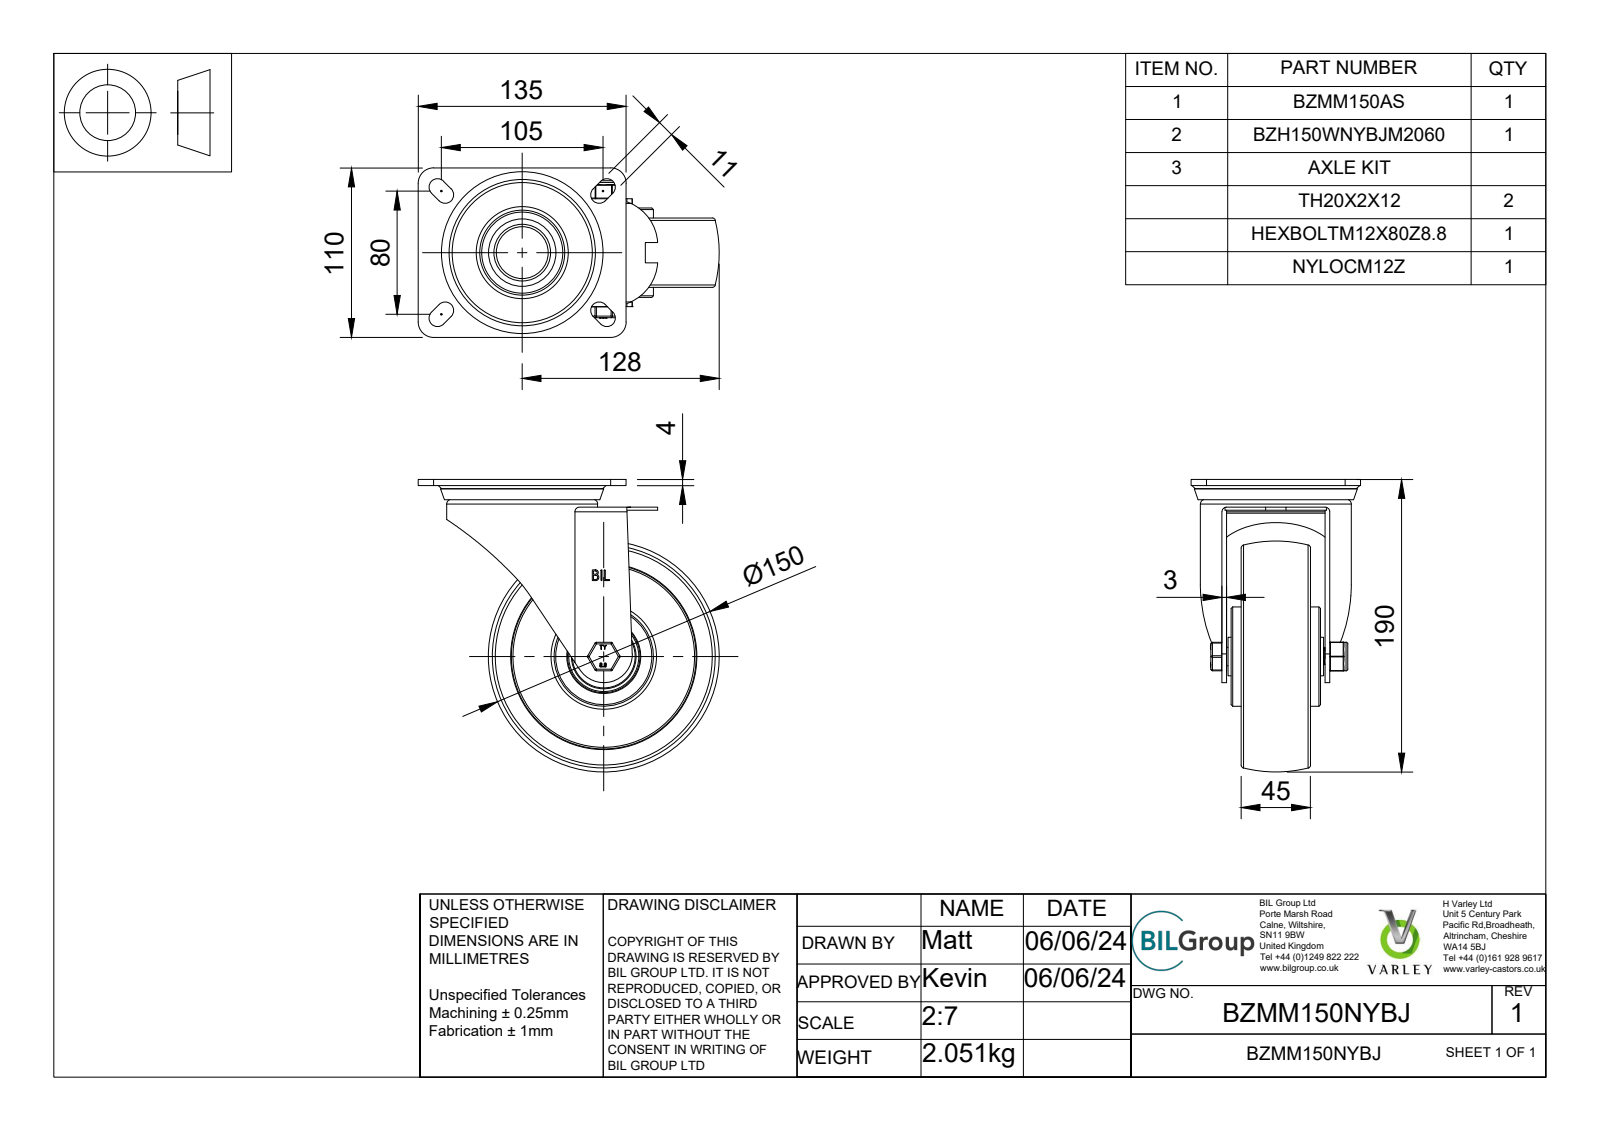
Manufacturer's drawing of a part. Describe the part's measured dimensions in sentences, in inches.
The part is named "BZMM150NYBJ v4; BZMM150AS - 2 - 64 v2; ZINC PLATED, PRESSED STEEL TOP PLATE; ZINC PLATED, PRESSED STEEL TOP PLATE Geometry (+7 more)". Its 3-D file was written by "Autodesk Translation Framework v13.14.0.145 (AUTOMOTIVE_DESIGN)". It is 76 solids with 1111 faces: 418 planar, 200 cylindrical and 493 other. Overall it measures 7.697 by 7.48 by 4.331 inches. Its volume is 40.5 cubic inches and its surface area 366 square inches. Round holes: 1 of diameter 0.472, 1 of diameter 0.48, 1 of diameter 0.551, 1 of diameter 0.787, 1 of diameter 0.846, 1 of diameter 1.122, 1 of diameter 1.213, 1 of diameter 1.329, 1 of diameter 1.565, 1 of diameter 1.587, 1 of diameter 1.594, 1 of diameter 1.614. Round bosses or shafts: 1 of diameter 3.858, 1 of diameter 3.071, 1 of diameter 2.539, 1 of diameter 1.969, 1 of diameter 1.606, 1 of diameter 1.232, 1 of diameter 1.063, 1 of diameter 1. Partial cylindrical surfaces (rounded edges, fillets, slot ends): 18 of radius 0.02, 12 of radius 0.039, 8 of radius 0.217, 4 of radius 0.394, 2 of radius 0.059, 2 of radius 0.118, 2 of radius 1.18, 1 of radius 0.65. The main face-to-face distances are 0.118, 0.354, 0.157, 0.394, 0.197, 0.276, 2.264, 0.492, 1.181, 0.079.
